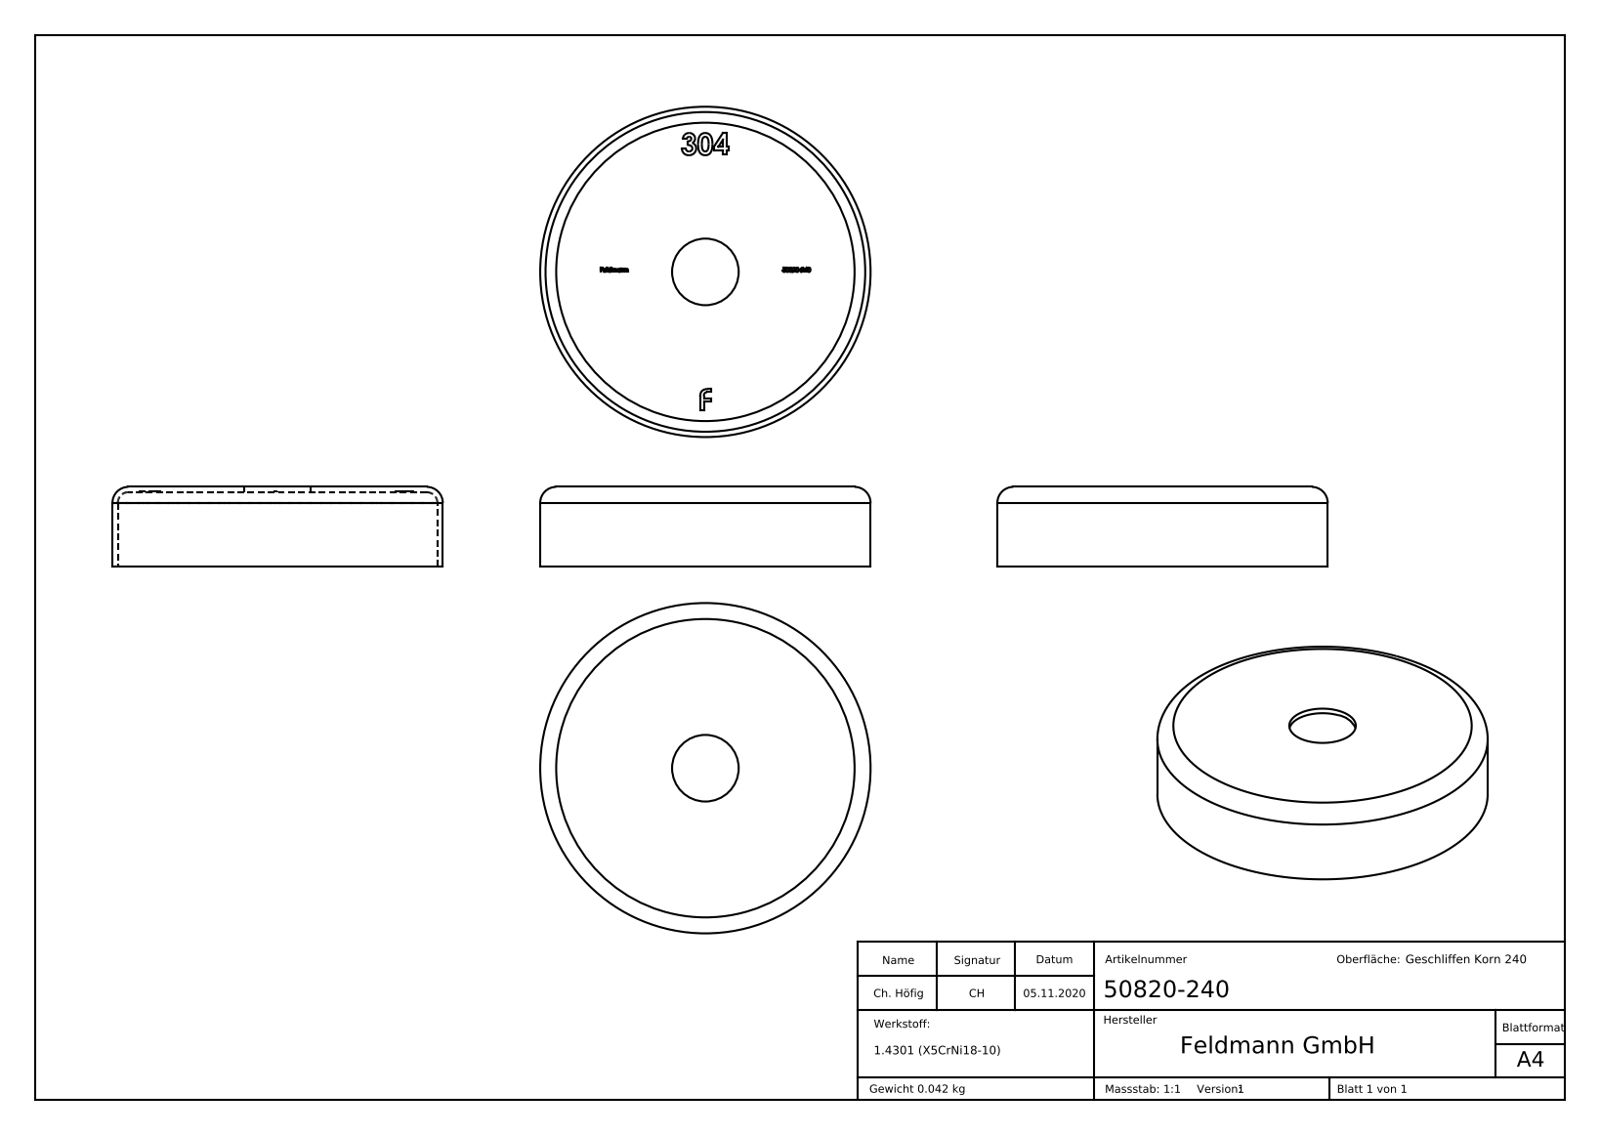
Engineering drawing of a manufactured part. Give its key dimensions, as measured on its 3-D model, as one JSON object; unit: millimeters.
{"part_name": "50820-240", "step_written_by": "SolidWorks 2018 (CONFIG_CONTROL_DESIGN)", "units": "millimeters", "bodies": {"solids": 1, "faces": 298, "planar": 151, "cylindrical": 6, "other": 141}, "overall_size": [62, 62, 15], "volume_mm3": 5368, "surface_area_mm2": 10987, "round_holes": [[12.5, 1], [60, 1]], "round_bosses_or_shafts": [[62, 1]], "face_to_face_distances": [1, 15, 14, 14.1, 0.9, 0.71, 5, 4.29, 0.58, 0.69]}
